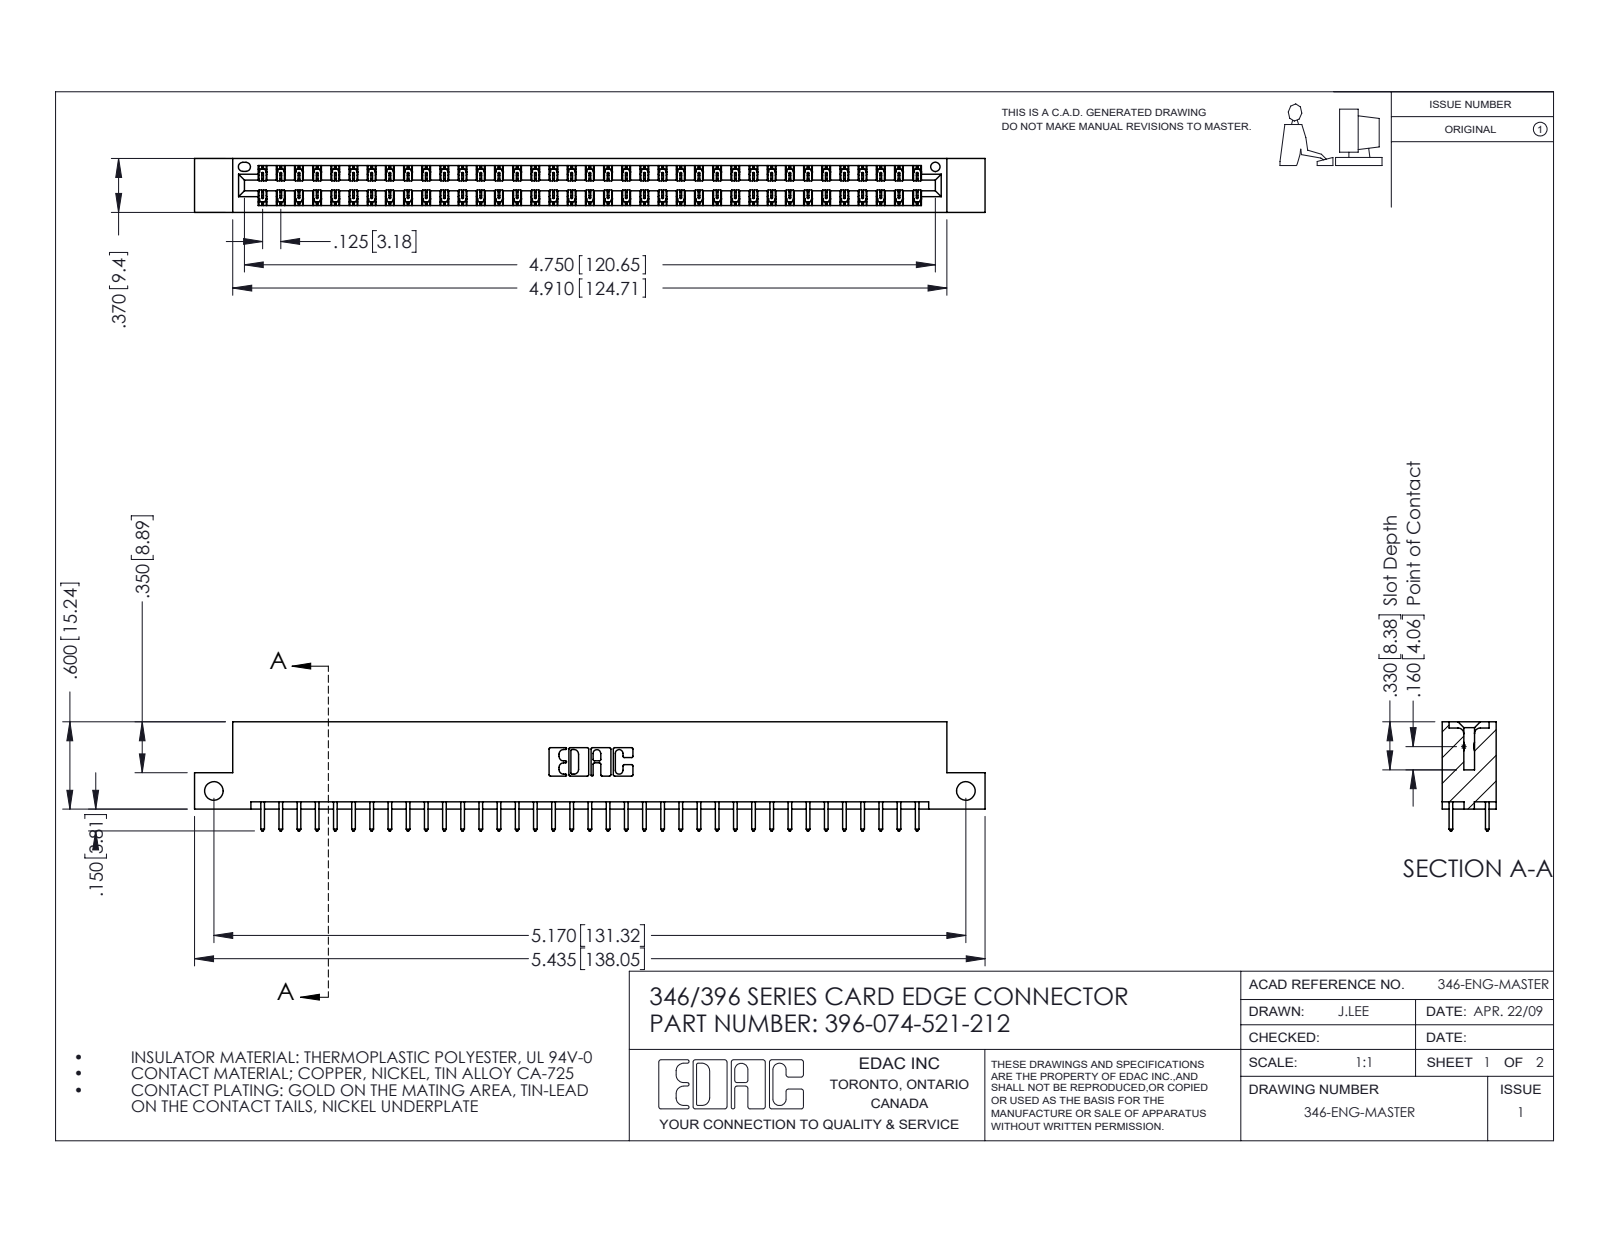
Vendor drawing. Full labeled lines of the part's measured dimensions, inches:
Part name (STEP PRODUCT): 345-292-001_345-293-121; 346 Part_Flush Mounting Lugs - Side Mount; 396-074-521-212
STEP written by: SolidWorks 2016 (CONFIG_CONTROL_DESIGN)
Units: inches
Bodies: 75 solids, 3970 faces (2666 planar, 1304 cylindrical, 0 other)
Overall size (bounding box): 5.435 × 0.75 × 0.37
Volume: 0.812 in³ · Surface area: 27.7 in²
Round holes (diameter × count): ⌀0.128 ×2, ⌀0.064 ×1
Partial cylindrical surfaces — rounded edges, fillets, slot ends (radius × count): R0.006 ×111, R0.01 ×74, R0.01 ×22, R0.007 ×6, R0.031 ×6, R0.026 ×3, R0.014 ×2, R0.022 ×2
Main face-to-face distances: 0.048, 0.322, 0.25, 0.37, 0.072, 0.298, 0.025, 0.275, 0.148, 0.222
Hole centre spacings: 5.17
